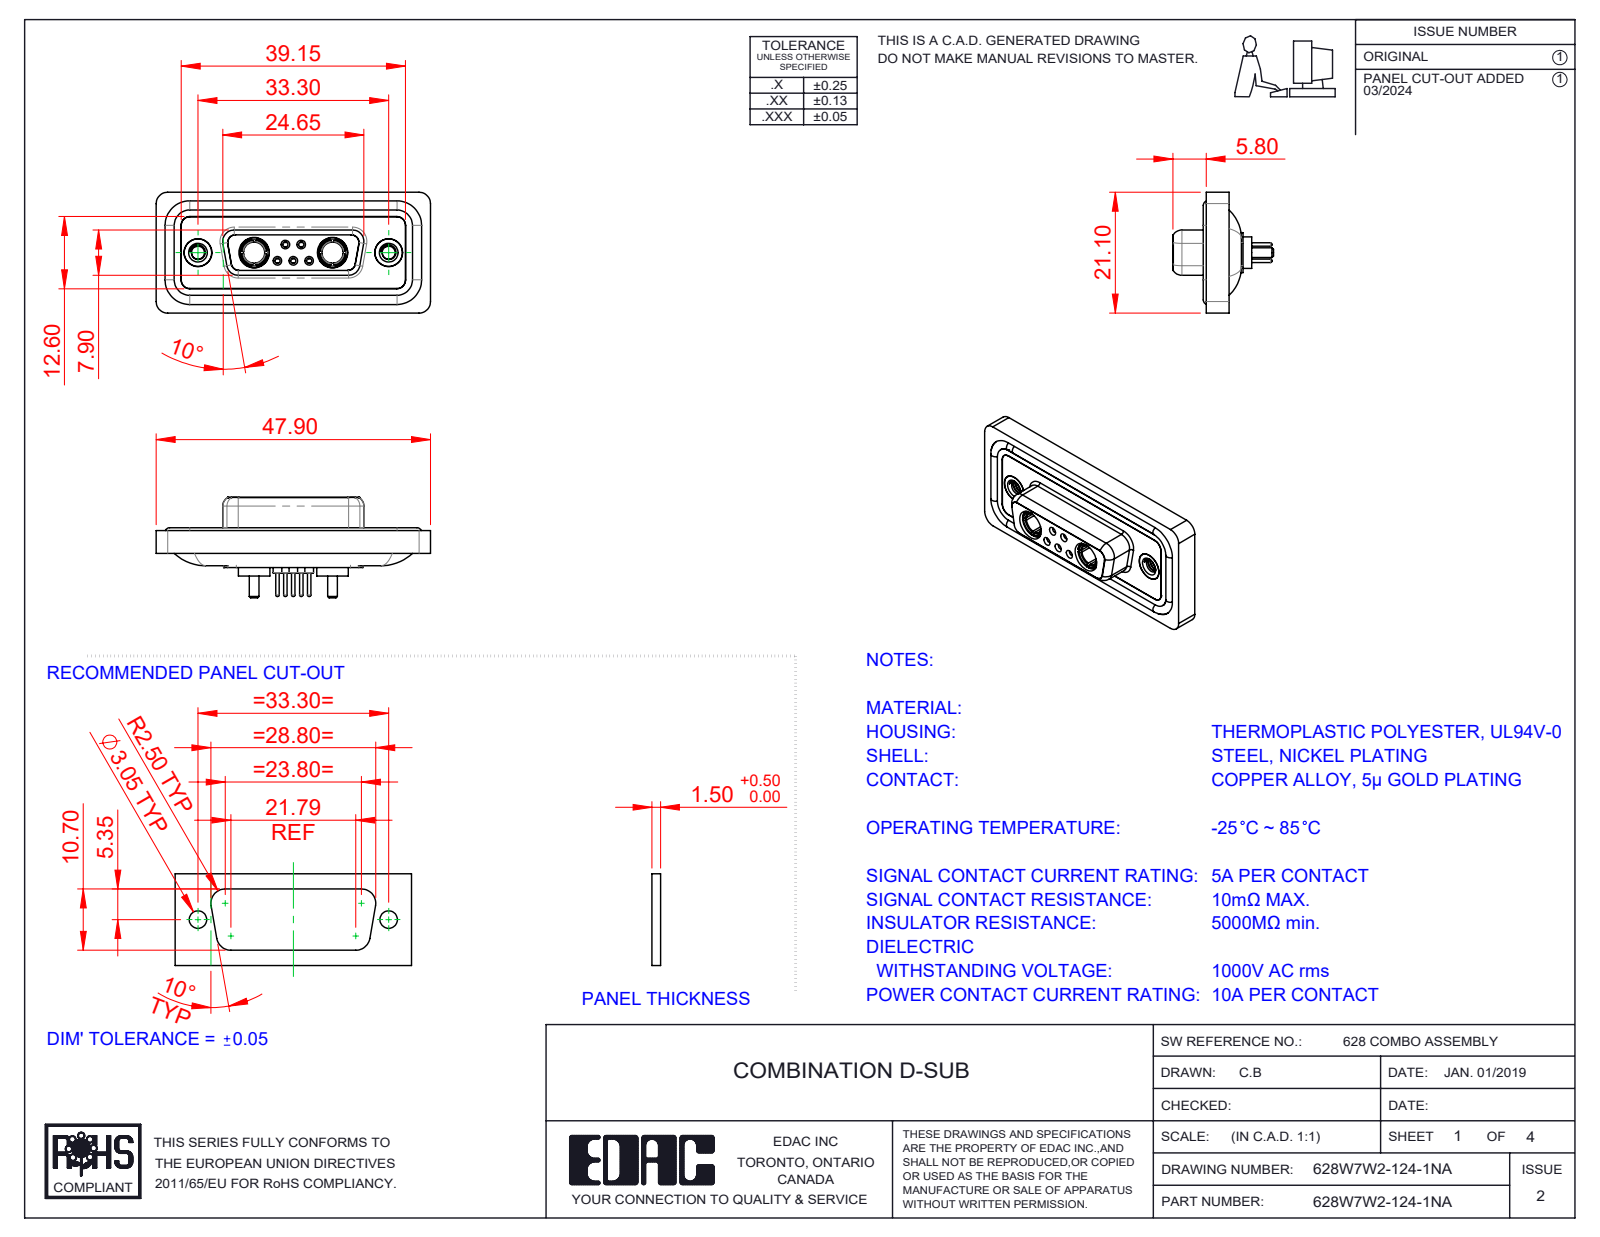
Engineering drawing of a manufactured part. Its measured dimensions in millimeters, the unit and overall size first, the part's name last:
Units: millimetres
Overall size (bounding box): 47.9 × 21.1 × 17.55
Round holes (diameter × count): ⌀0.9 ×5, ⌀1.1 ×5, ⌀1.5 ×5, ⌀2 ×5, ⌀4.85 ×4, ⌀1.6 ×3, ⌀1.7 ×2, ⌀2.26 ×2, ⌀3.7 ×2, ⌀4 ×2, ⌀4.05 ×2, ⌀5 ×2
Round bosses / shafts (diameter × count): ⌀1.6 ×6, ⌀2.2 ×5, ⌀0.6 ×5, ⌀5.5 ×2, ⌀5.2 ×2, ⌀4.96 ×2, ⌀4.95 ×2, ⌀4.8 ×2
Partial cylindrical surfaces — rounded edges, fillets, slot ends (radius × count): R1.5 ×22, R2 ×20, R1.35 ×12, R1.6 ×8, R0.25 ×4, R0.5 ×4, R0.6 ×4, R0.65 ×4
Main face-to-face distances: 0.4, 1.8, 1.6, 0.5, 2.9, 1.1, 7.45, 5.65, 6.6, 7.05
Hole centre spacings: 3.16, 2.77, 9.8, 23.5, 4.31, 4.33, 5.03, 5.04
Volume: 6 049 mm³ · Surface area: 9 857 mm²
Bodies: 16 solids, 807 faces (238 planar, 331 cylindrical, 238 other)
Part name (STEP PRODUCT): 628Combo Shell Rear_15 Contacts; 628W7W2-124-1NA; 628Combo Waterproof Housing_15 Contacts; 628Combo Threaded Rivet_A (+5 more)
STEP written by: SolidWorks 2023 (CONFIG_CONTROL_DESIGN)
